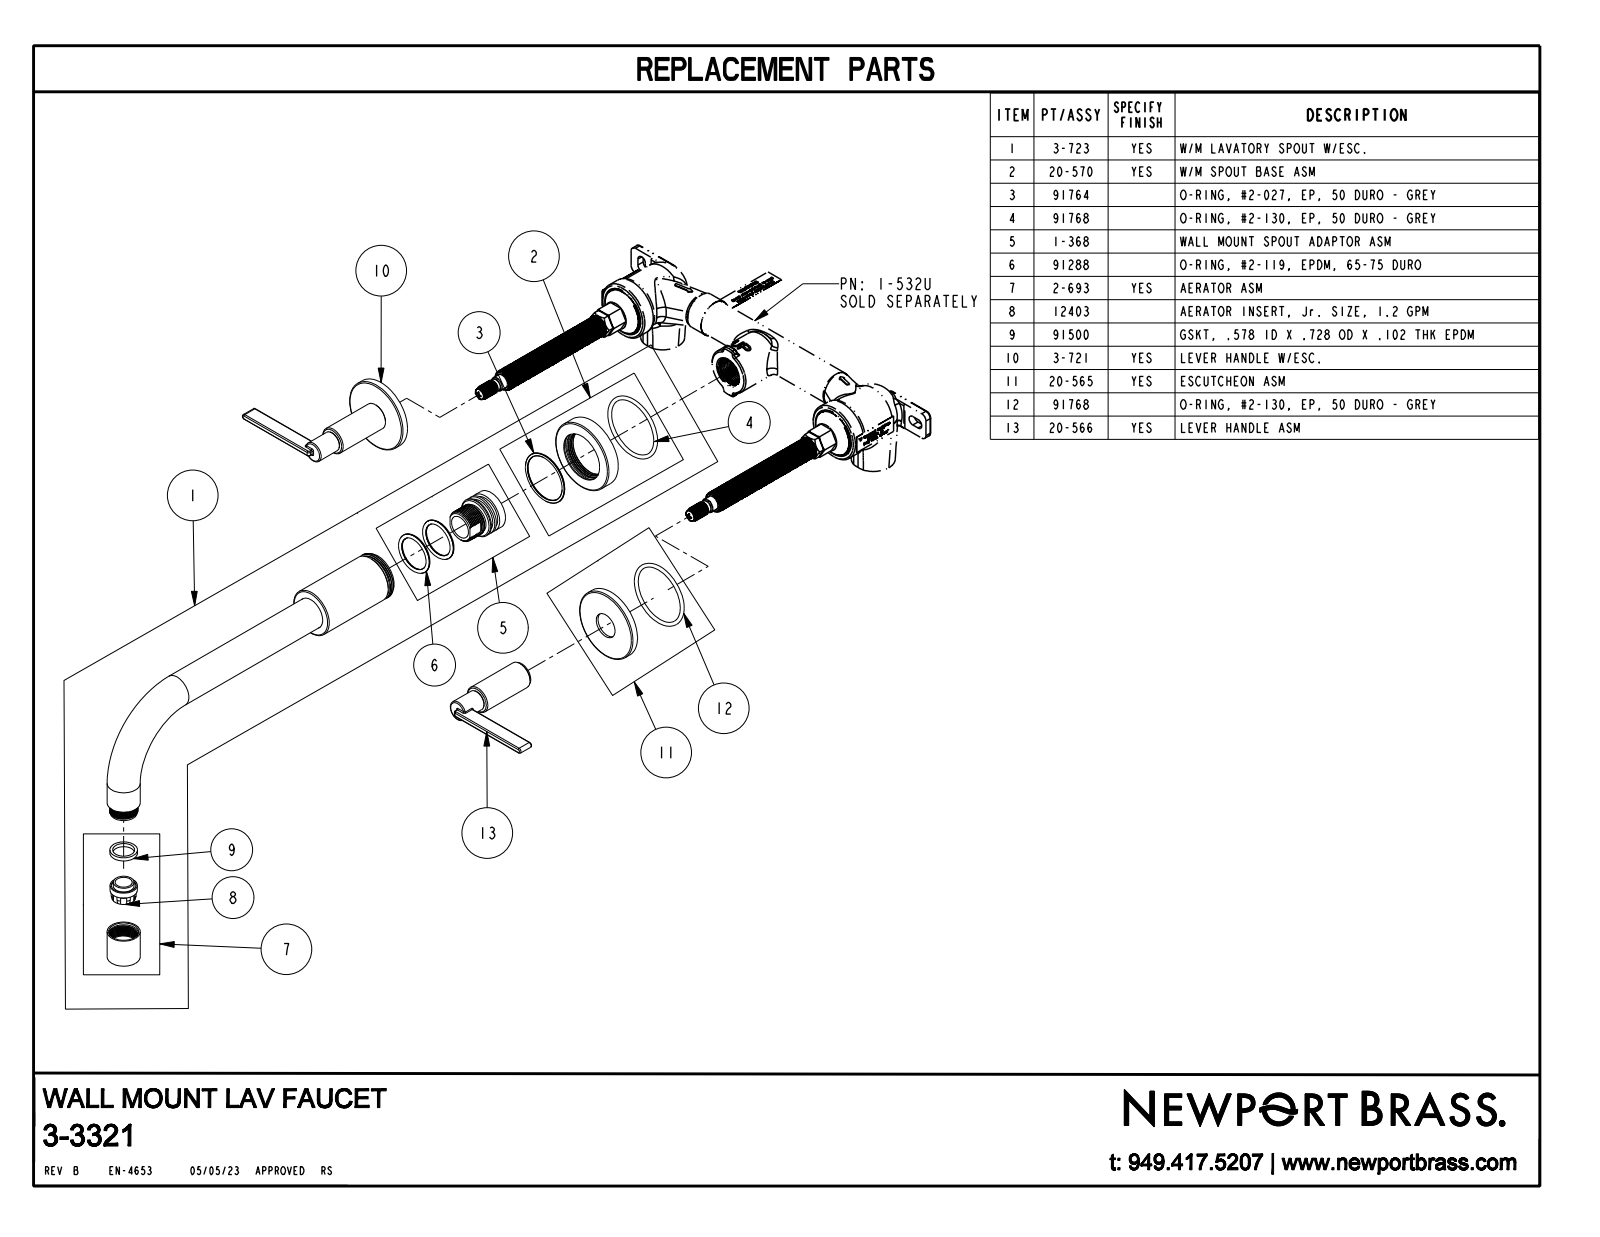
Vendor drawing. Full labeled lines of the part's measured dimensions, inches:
Part name (STEP PRODUCT): 13414; 10624; 20-533_ASM; 13538 (+8 more)
STEP written by: CREO PARAMETRIC BY PTC INC, 2018400 (CONFIG_CONTROL_DESIGN)
Units: inches
Bodies: 11 solids, 639 faces (171 planar, 313 cylindrical, 155 other)
Overall size (bounding box): 12.874 × 8.687 × 4.49
Volume: 5.802 in³ · Surface area: 121.2 in²
Round holes (diameter × count): ⌀1.6 ×3, ⌀0.11 ×2, ⌀0.36 ×2, ⌀0.397 ×2, ⌀0.4 ×2, ⌀0.516 ×2, ⌀0.535 ×2, ⌀0.6 ×2, ⌀0.7 ×2, ⌀0.751 ×2, ⌀1.89 ×2, ⌀0.56 ×1
Round bosses / shafts (diameter × count): ⌀2 ×2, ⌀1.65 ×2, ⌀0.875 ×2, ⌀0.75 ×2, ⌀0.73 ×2, ⌀0.68 ×2, ⌀0.563 ×2, ⌀0.51 ×2
Partial cylindrical surfaces — rounded edges, fillets, slot ends (radius × count): R0.03 ×16, R0.06 ×2, R0.075 ×2, R0.137 ×2, R0.34 ×1
Main face-to-face distances: 0.05, 0.15, 0.12, 0.295, 0.07, 0.2, 0.225, 0.175, 0.08, 0.375
Hole centre spacings: 3.937, 7.874
